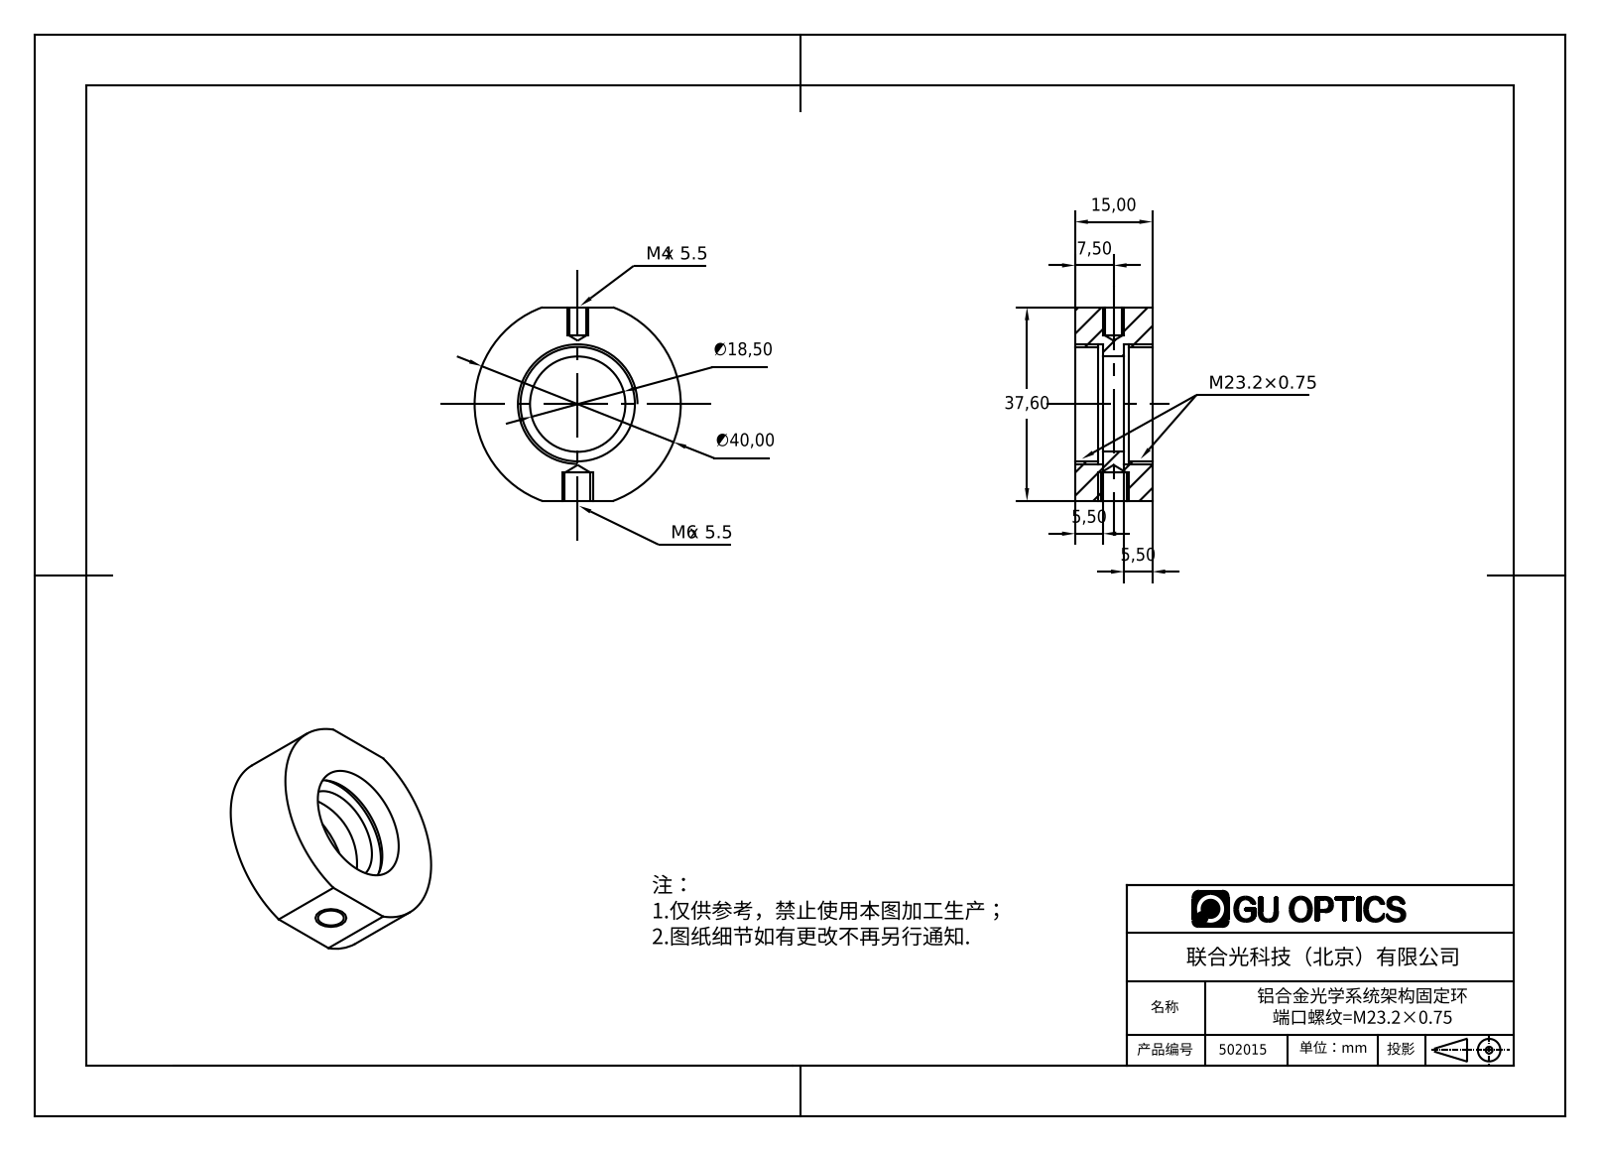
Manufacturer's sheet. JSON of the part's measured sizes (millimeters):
{"part_name": "502015", "step_written_by": "SolidWorks 2016 (CONFIG_CONTROL_DESIGN)", "units": "millimeters", "bodies": {"solids": 1, "faces": 29, "planar": 8, "cylindrical": 17, "other": 4}, "overall_size": [40, 37.6, 15], "volume_mm3": 12933, "surface_area_mm2": 5136, "round_holes": [[3.3, 1], [5, 1], [18.5, 1], [22.2, 1], [23.4, 1]], "partial_cylinders_radius": [[20, 1]], "face_to_face_distances": [15, 5.5, 9.5, 37.6, 4, 4.5, 10.5, 1, 5, 6]}
